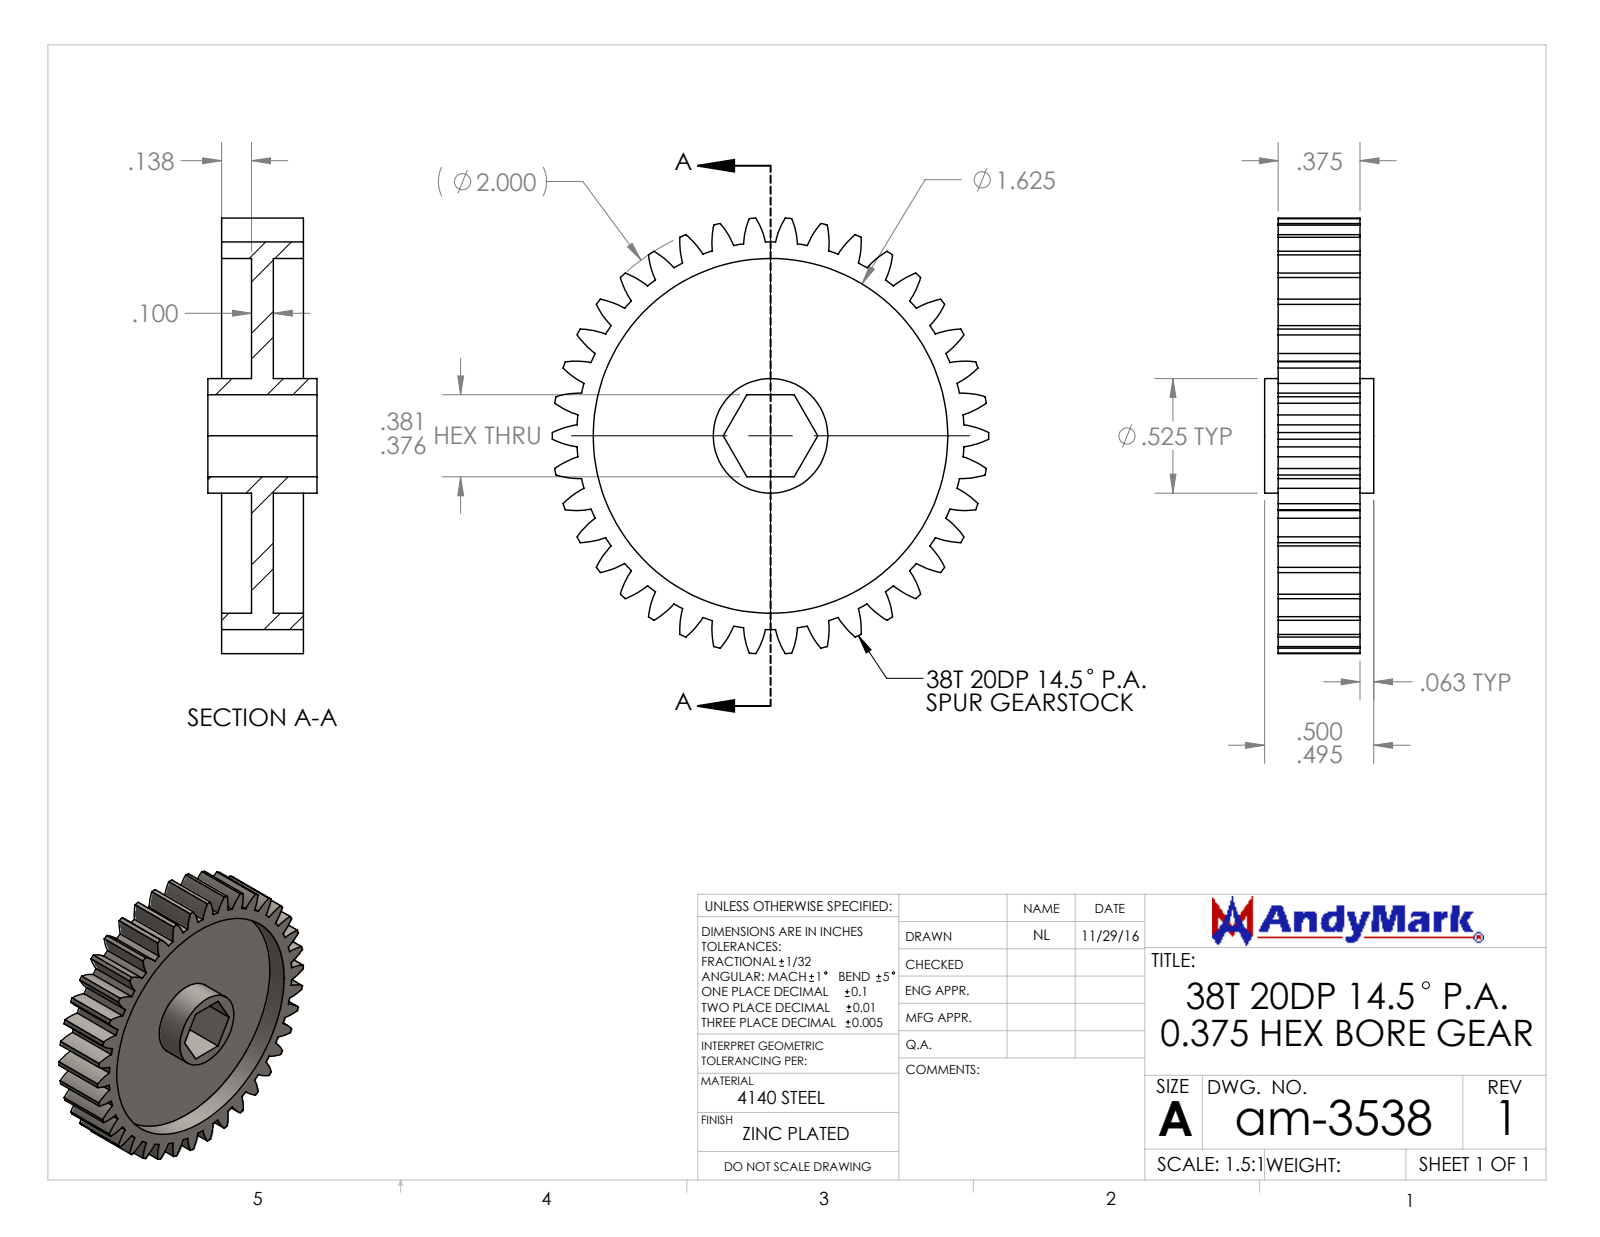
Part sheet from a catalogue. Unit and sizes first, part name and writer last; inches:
Units: inches
Overall size (bounding box): 2 × 1.995 × 0.5
Round holes (diameter × count): ⌀1.625 ×1
Round bosses / shafts (diameter × count): ⌀0.525 ×1
Partial cylindrical surfaces — rounded edges, fillets, slot ends (radius × count): R0.38 ×76, R0.888 ×1, R1 ×1
Main face-to-face distances: 0.1, 0.238, 0.138, 0.137, 0.237, 0.375, 0.376, 0.2, 0.3, 0.063
Volume: 0.499 in³ · Surface area: 12.52 in²
Bodies: 1 solid, 177 faces (12 planar, 165 cylindrical, 0 other)
Part name (STEP PRODUCT): am-3538 38T 20DP 375Hex 375 FW
STEP written by: SolidWorks 2014 (AUTOMOTIVE_DESIGN)
